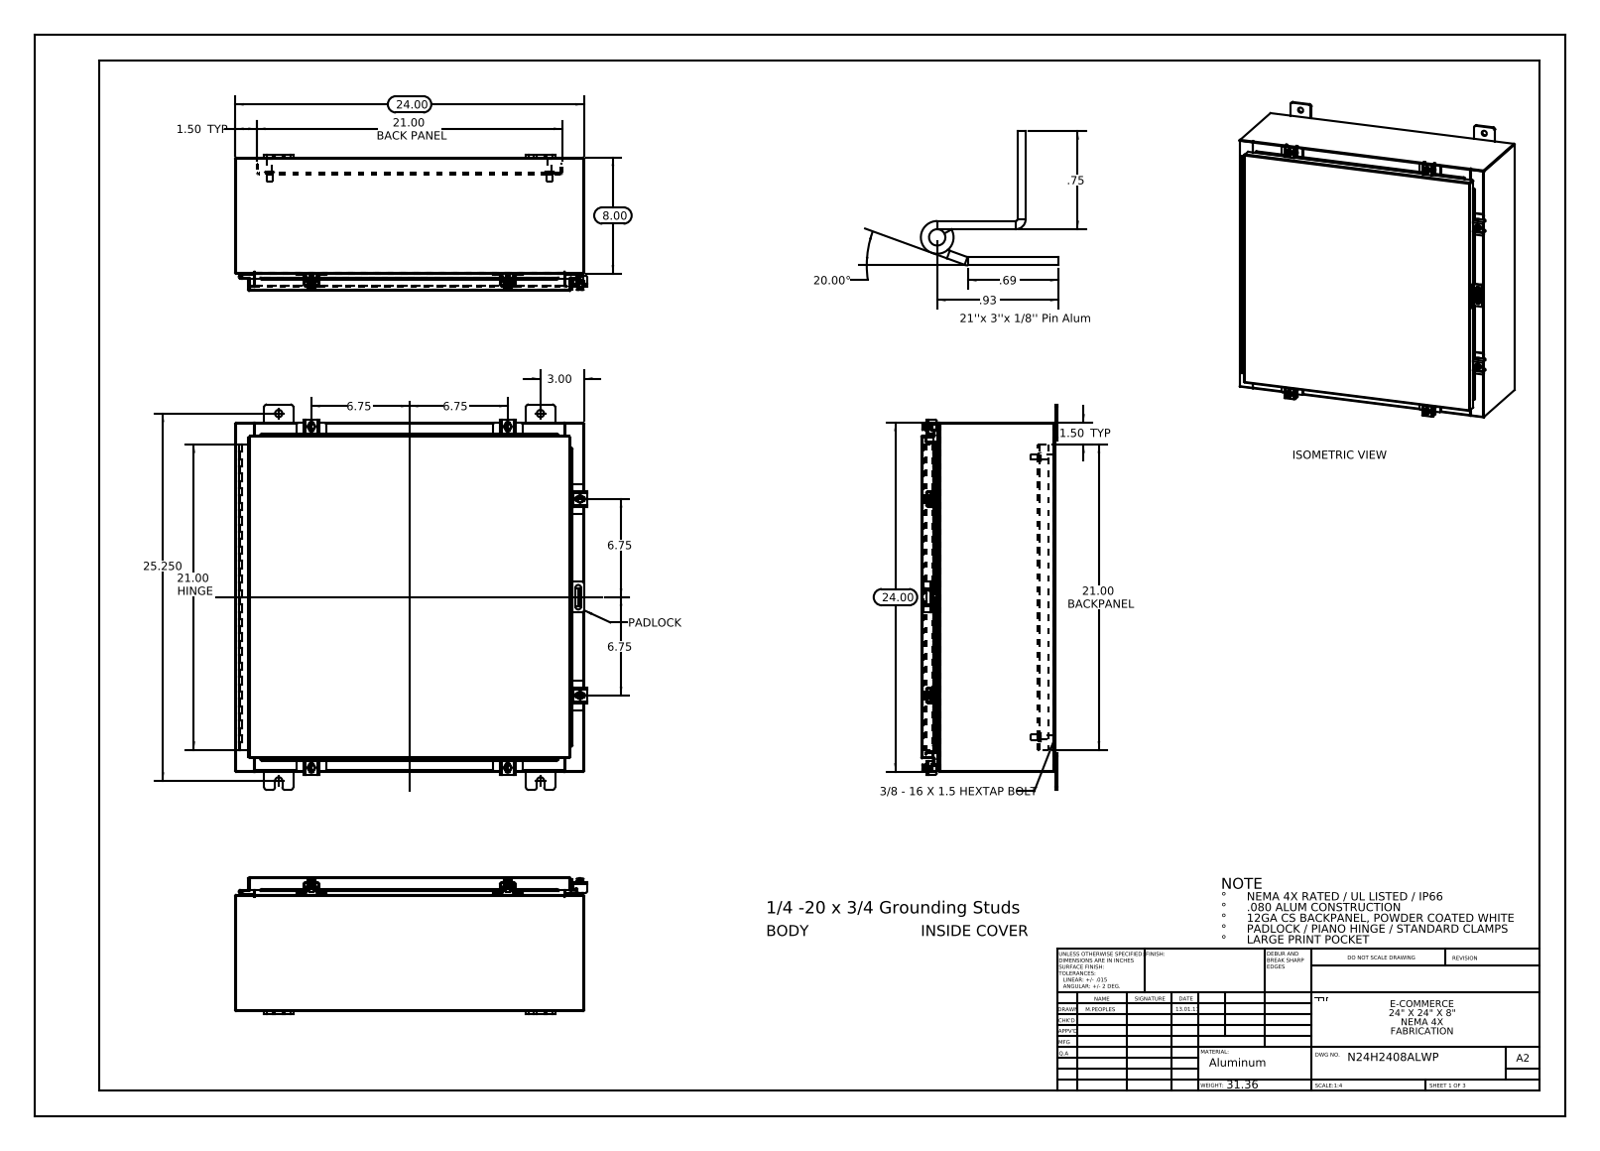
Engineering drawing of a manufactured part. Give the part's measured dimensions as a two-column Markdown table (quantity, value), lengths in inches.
| quantity | value |
| --- | --- |
| part name | N24H2408ALWP Backpanel; N24H2408ALWP Hinge Cover Side; N24H2408ALWP Clamp Bracket; N24H2408ALWP Top (+8 more) |
| STEP written by | SolidWorks 2013 (CONFIG_CONTROL_DESIGN) |
| units | inches |
| bodies | 47 solids, 1709 faces (908 planar, 705 cylindrical, 96 other) |
| overall size | 26.5 × 24.211 × 9.389 |
| volume | 216.2 in³ |
| surface area | 5 431 in² |
| round holes (diameter × count) | 0.5 × 8, 0.213 × 6, 0.26 × 6, 0.125 × 2 |
| round bosses / shafts (diameter × count) | 0.25 × 7, 0.5 × 6, 0.399 × 6, 0.625 × 4, 0.375 × 4, 0.33 × 4 |
| partial cylindrical surfaces (radius × count) | 0.06 × 30, 0.013 × 25, 0.19 × 24, 0.088 × 21, 0.12 × 12, 0.141 × 12, 0.125 × 10, 0.05 × 9 |
| main face-to-face distances | 0.075, 9.126, 23.925, 9.201, 9.051, 0.104, 1, 1.075, 8.051, 8.126 |
| hole center spacings | 16.509, 19.134, 21.544, 26.907, 13.5, 1.858, 2.277, 2.423 |
